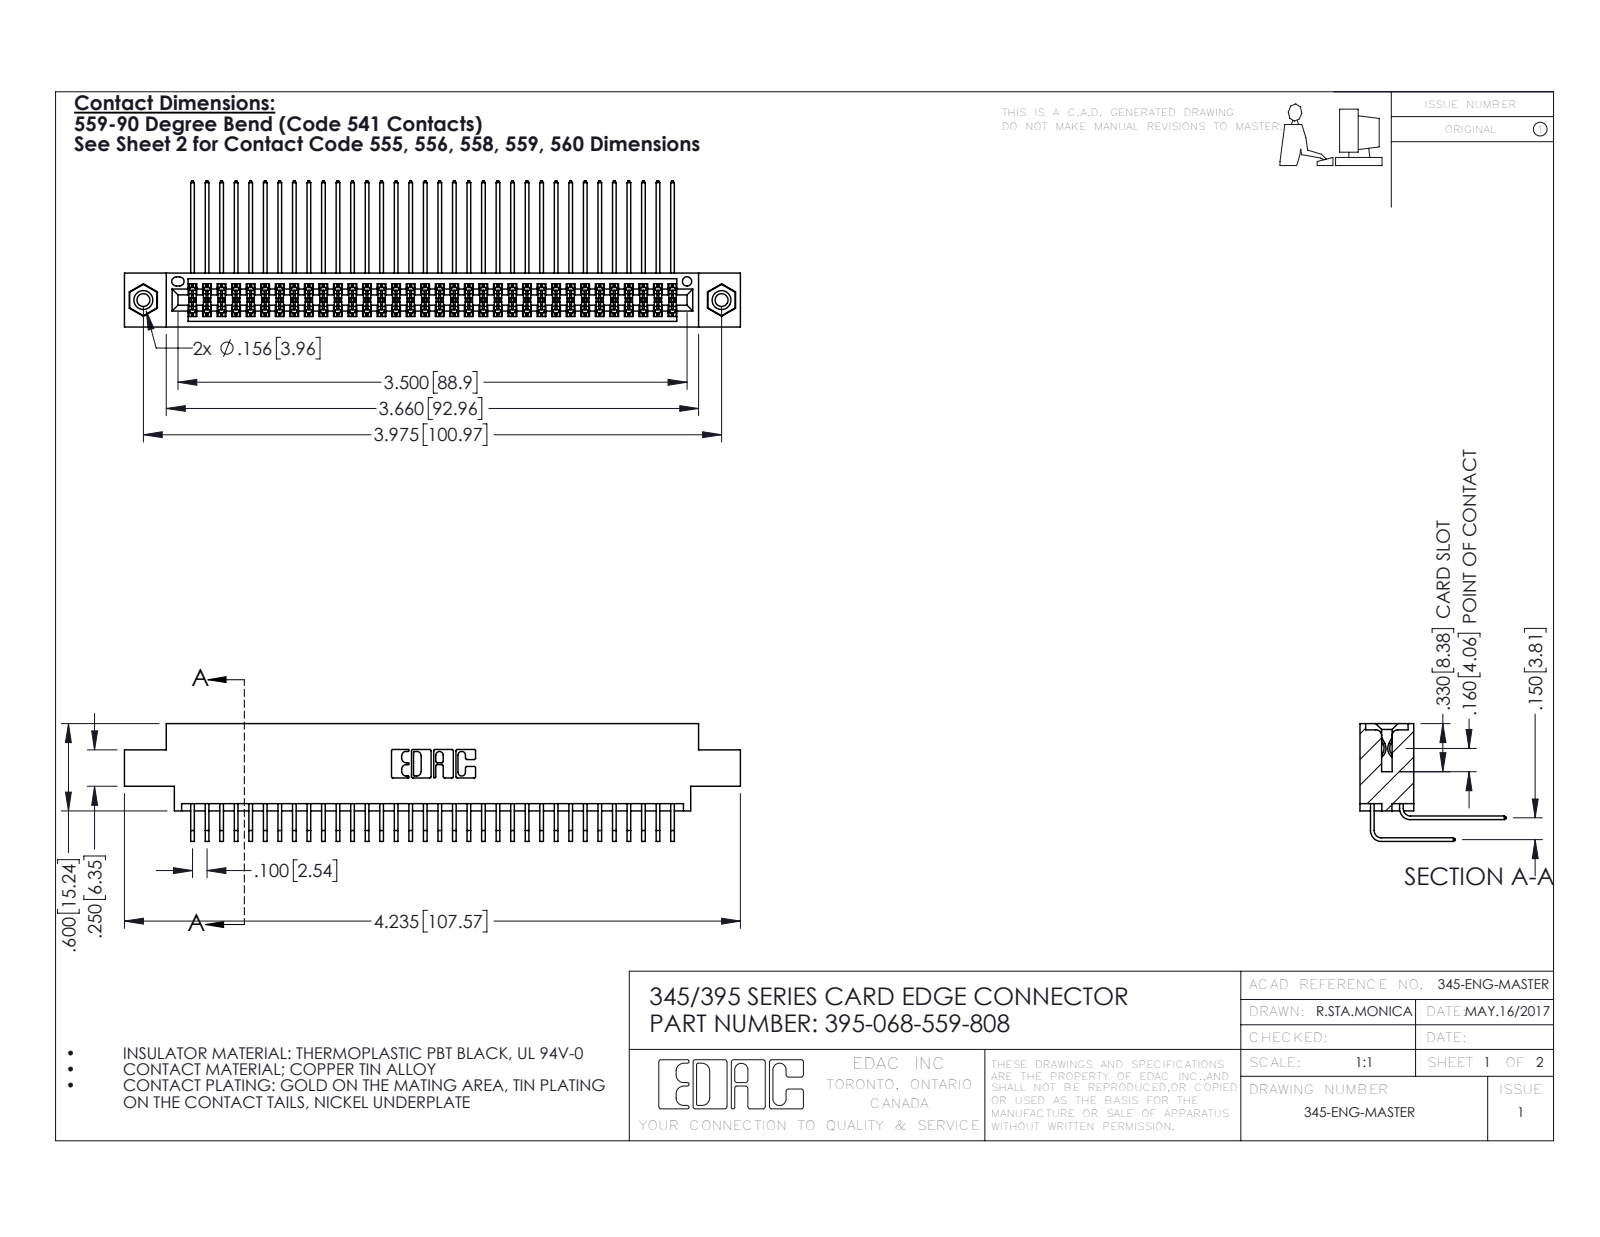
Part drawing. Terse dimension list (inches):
name: 345 Part_0.170 Offset - 0.156 Dia-TI; 345-292-001_559 Tail - 2; 345-250-001_345-250-003-102; 395-068-559-808 (+1 more)
written by: SolidWorks 2016 (CONFIG_CONTROL_DESIGN)
unit: in
bodies: 71 solids, 3726 faces (2496 planar, 1214 cylindrical, 16 other)
size: 4.235 × 1.005 × 0.809
volume: 0.65 in³; area: 27.26 in²
holes: 2× ⌀0.089, 2× ⌀0.125, 2× ⌀0.156, 1× ⌀0.064
bosses: 2× ⌀0.155
rounds: 103× R0.006, 22× R0.01, 6× R0.007, 6× R0.031, 3× R0.026, 2× R0.014, 2× R0.019, 2× R0.022
face distances: 0.072, 0.298, 0.37, 0.2, 0.098, 0.272, 0.025, 0.225, 0.175, 0.15
hole spacings: 0.27, 3.74, 3.975
